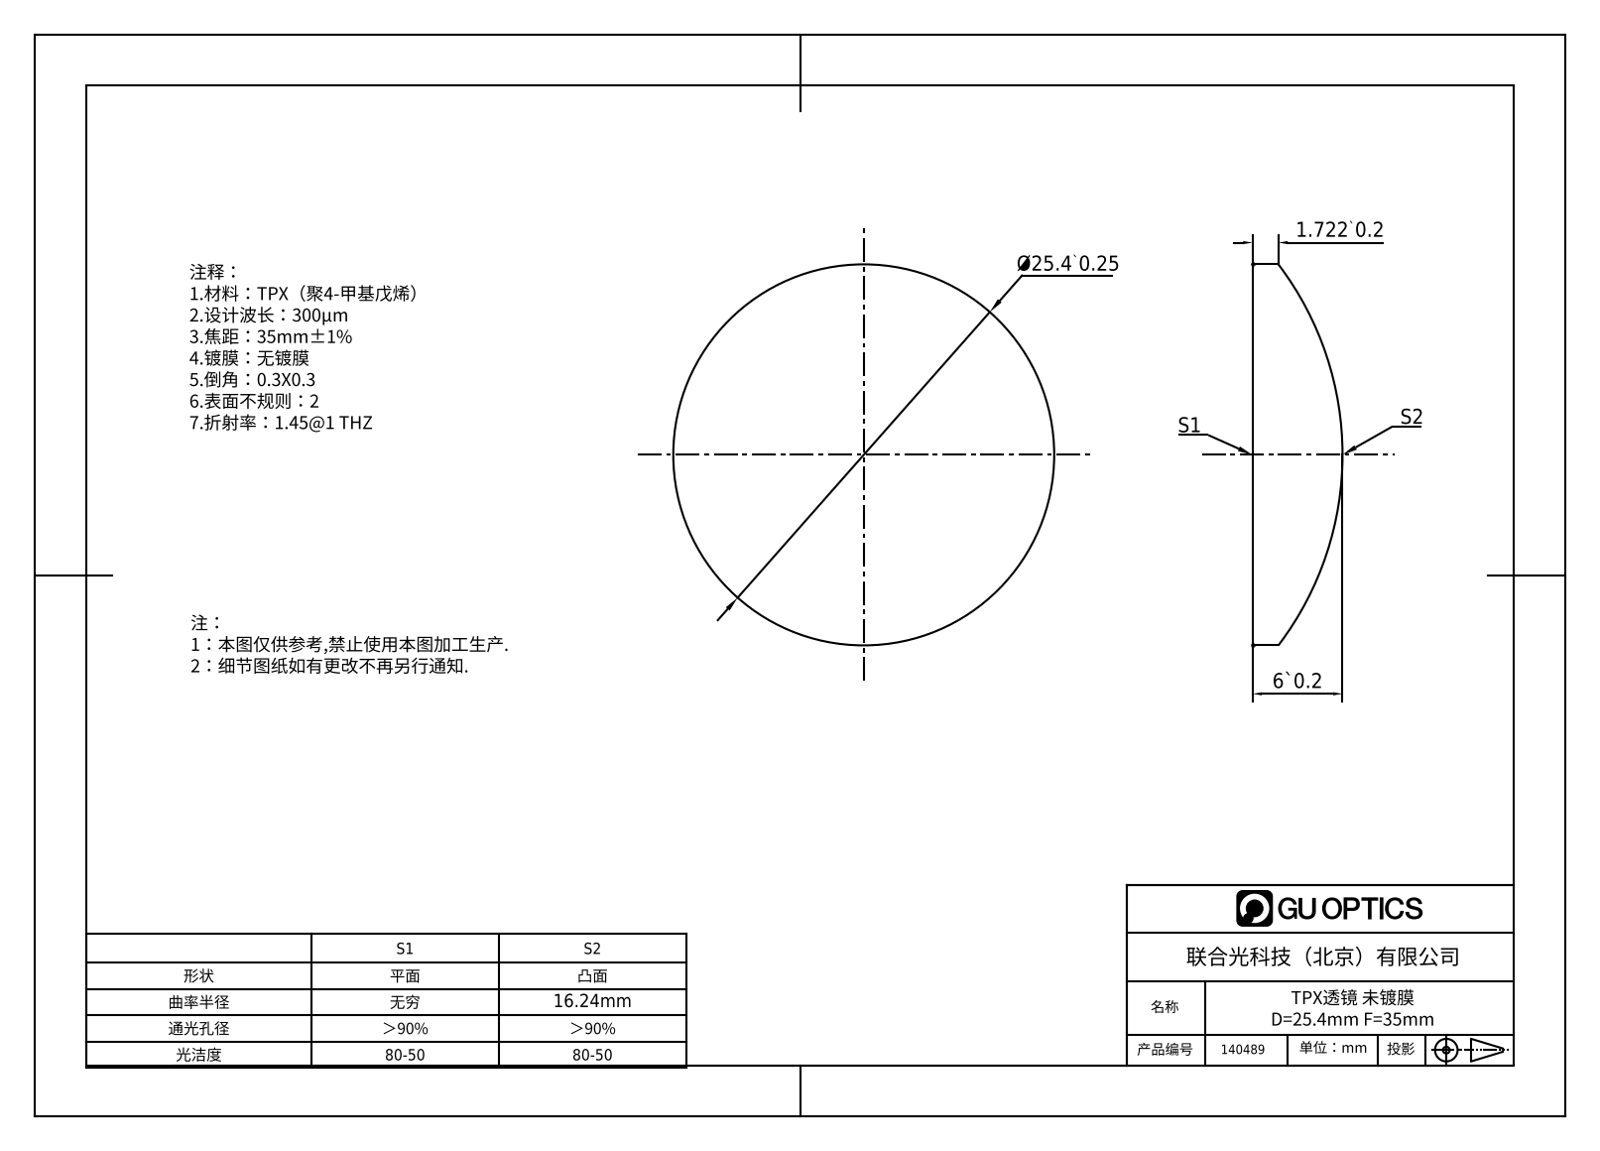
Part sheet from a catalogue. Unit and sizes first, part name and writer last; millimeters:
Units: millimetres
Overall size (bounding box): 25.4 × 25.4 × 6
Round bosses / shafts (diameter × count): ⌀25.4 ×1
Volume: 1 997 mm³ · Surface area: 1 208 mm²
Bodies: 1 solid, 5 faces (1 planar, 2 cylindrical, 2 other)
Part name (STEP PRODUCT): 140489
STEP written by: SolidWorks 2020 (AUTOMOTIVE_DESIGN)
